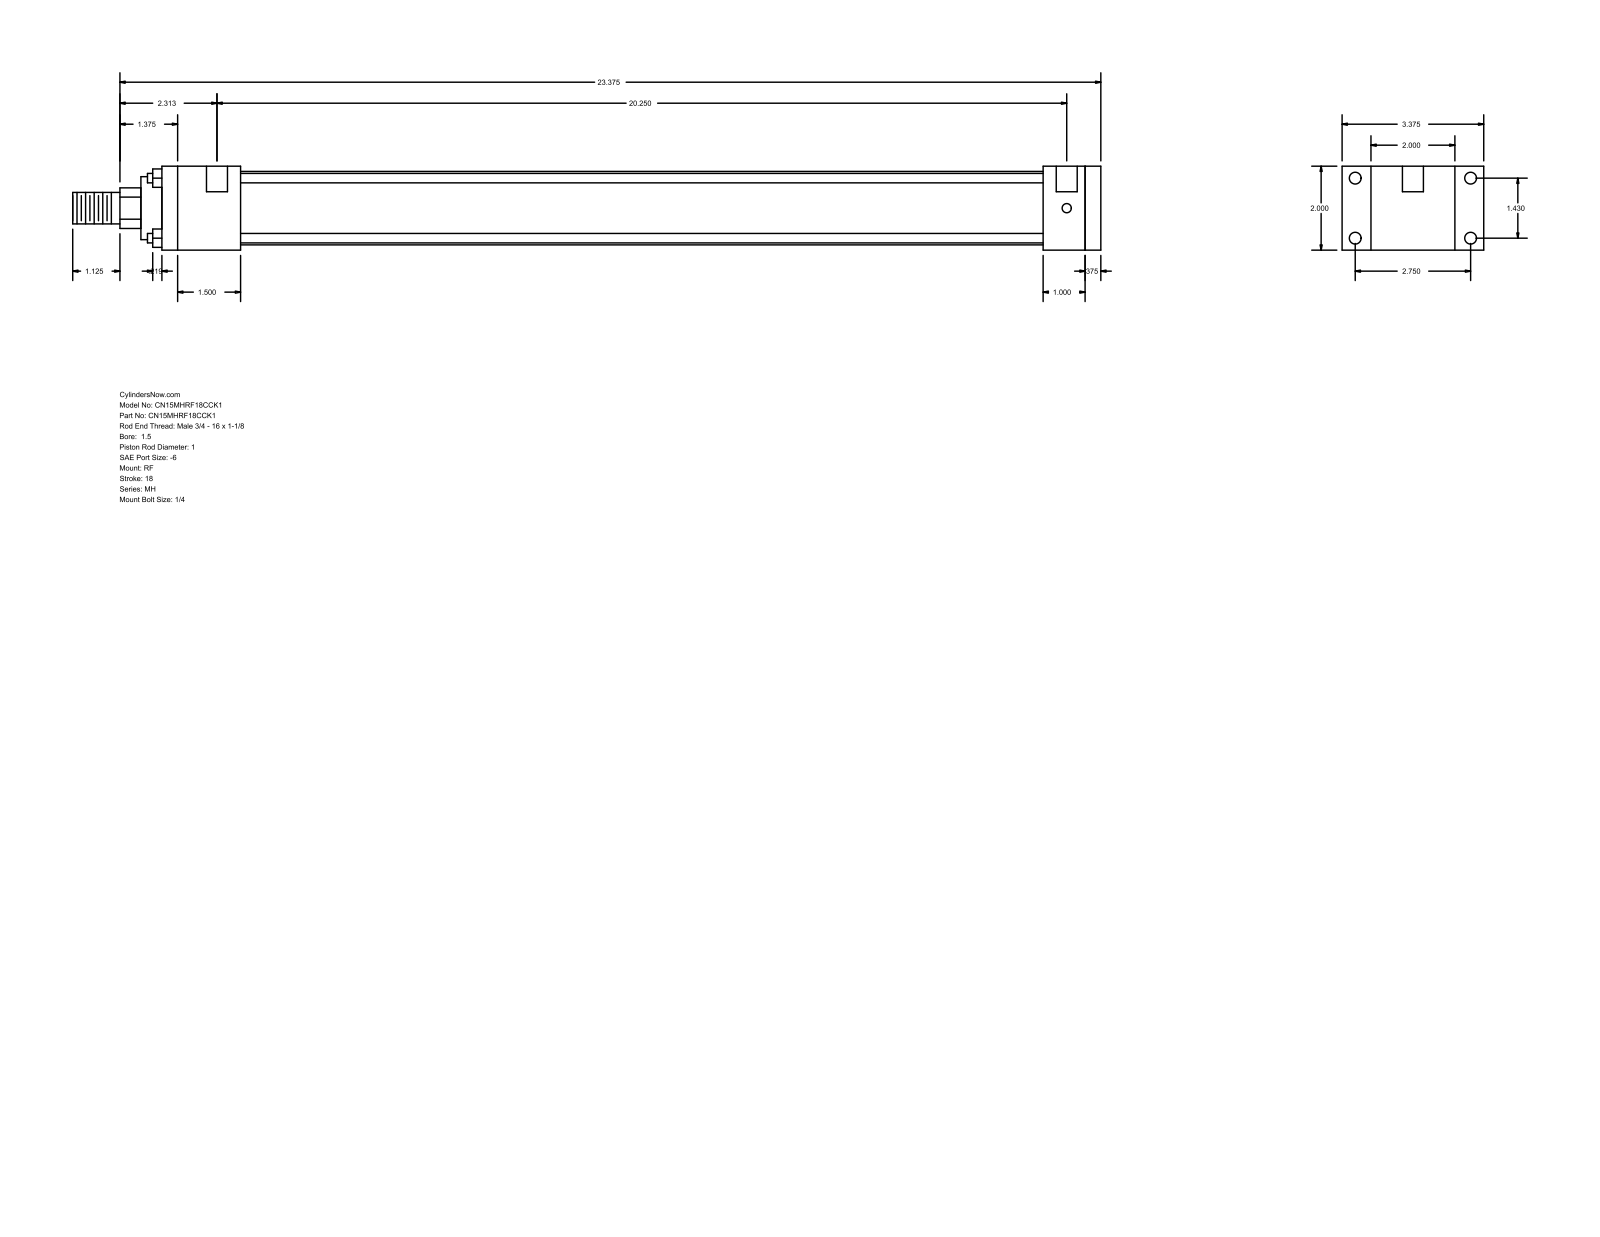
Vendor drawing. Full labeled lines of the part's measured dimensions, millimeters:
Part name (STEP PRODUCT): MH_RF__0150_1
STEP written by: GSSL Pune (CONFIG_CONTROL_DESIGN)
Units: millimetres
Bodies: 0 solids, 92 faces (64 planar, 28 cylindrical, 0 other)
Overall size (bounding box): 622.3 × 85.72 × 50.8
Round holes (diameter × count): ⌀5.56 ×4, ⌀7.14 ×4, ⌀12.7 ×2
Round bosses / shafts (diameter × count): ⌀5.71 ×4, ⌀44.45 ×1, ⌀38.1 ×1, ⌀25.4 ×1, ⌀19.05 ×1
Partial cylindrical surfaces — rounded edges, fillets, slot ends (radius × count): R12.29 ×1
Main face-to-face distances: 50.8, 9.53, 558.8, 25.4, 568.33, 17.46, 68.26, 533.4, 34.93, 47.63
Hole centre spacings: 36.32, 69.84, 78.72, 517.53, 3.18, 514.35
